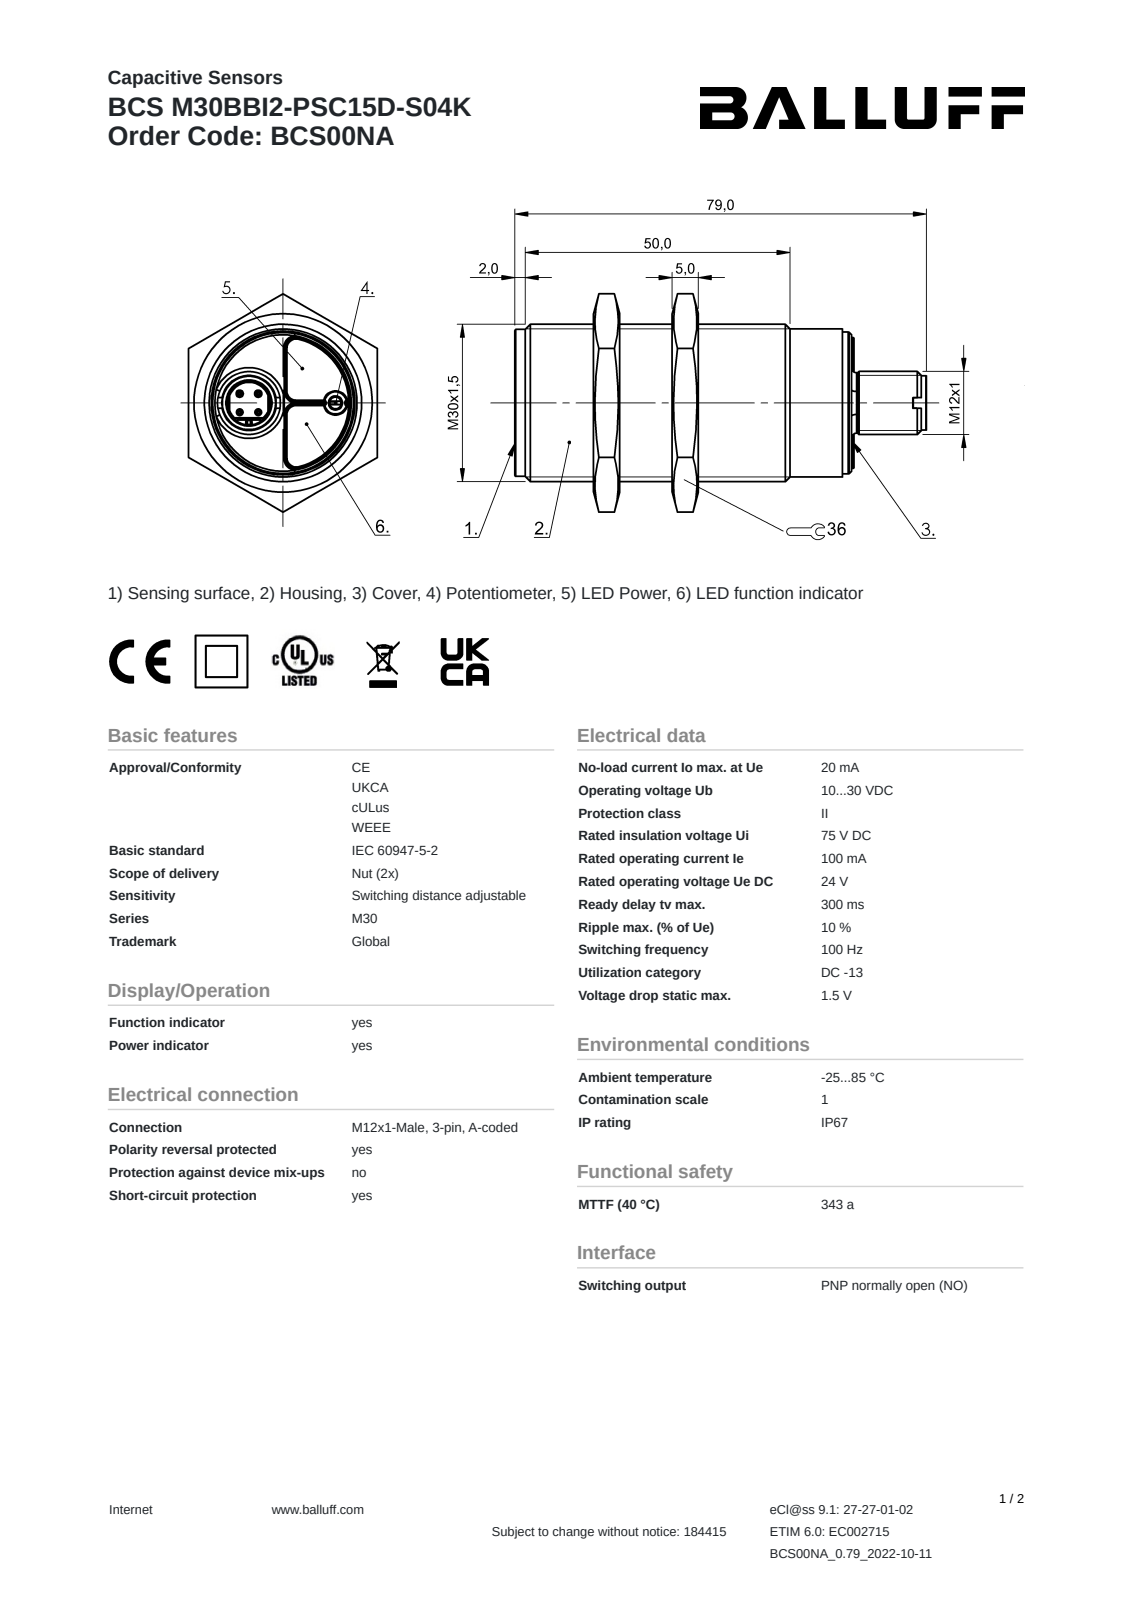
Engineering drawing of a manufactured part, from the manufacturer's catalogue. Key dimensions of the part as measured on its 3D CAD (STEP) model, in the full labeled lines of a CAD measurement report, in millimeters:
Part name (STEP PRODUCT): BCS00NA
STEP written by: SolidWorks 2021 (AUTOMOTIVE_DESIGN)
Units: millimetres
Bodies: 3 solids, 183 faces (72 planar, 52 cylindrical, 59 other)
Overall size (bounding box): 79 × 41.6 × 36
Volume: 49 910 mm³ · Surface area: 12 130 mm²
Round holes (diameter × count): ⌀2.7 ×1, ⌀8.4 ×1, ⌀28.4 ×1
Round bosses / shafts (diameter × count): ⌀1 ×4, ⌀30 ×1, ⌀28.2 ×1, ⌀28 ×1, ⌀27 ×1, ⌀12 ×1, ⌀11.5 ×1, ⌀10.3 ×1
Partial cylindrical surfaces — rounded edges, fillets, slot ends (radius × count): R0.1 ×8, R0.3 ×5, R0.2 ×2, R0.6 ×1, R1 ×1, R4 ×1, R4.2 ×1, R4.6 ×1
Main face-to-face distances: 15.2, 5, 36, 14.8, 30, 20.2, 35, 10.2, 19.8, 29.7
Hole centre spacings: 6.5, 9.7, 16.2
